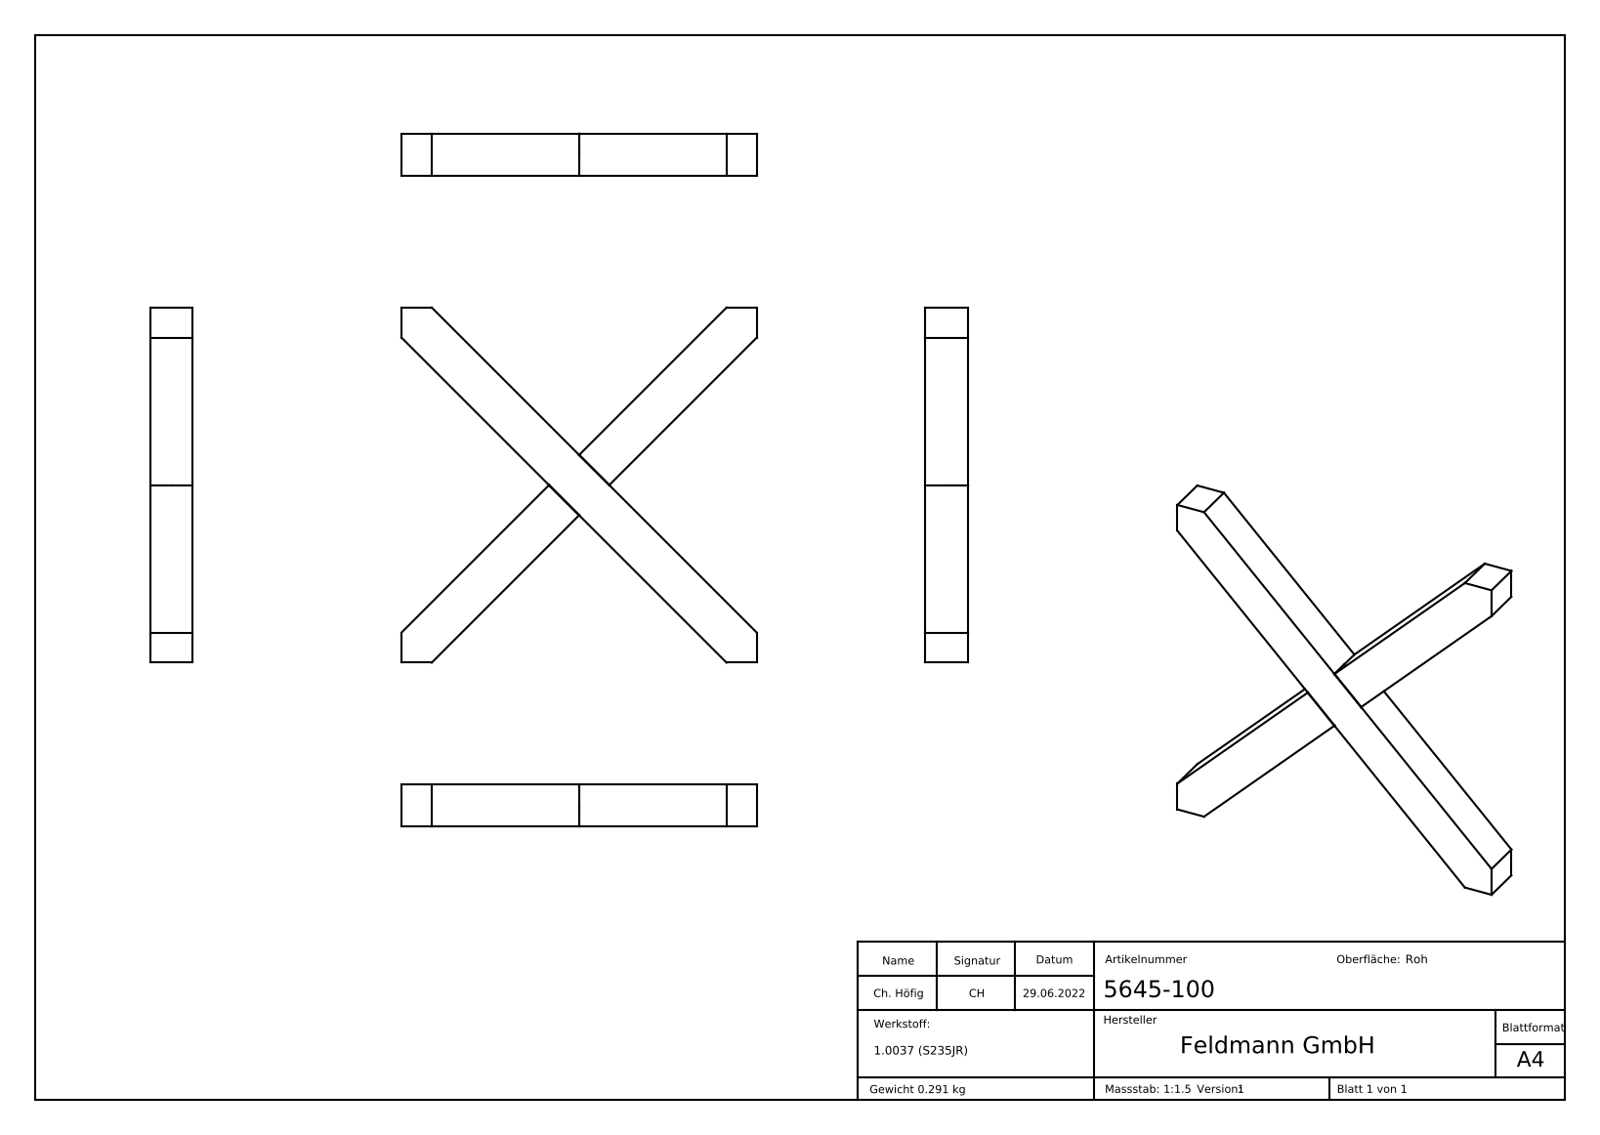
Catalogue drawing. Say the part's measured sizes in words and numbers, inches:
The part is named "5645-100". Its 3-D file was written by "SolidWorks 2018 (CONFIG_CONTROL_DESIGN)". It is 1 solid with 279 faces: 168 planar, 0 cylindrical and 111 other. Overall it measures 3.937 by 3.937 by 0.472 inches. Its volume is 2.274 cubic inches and its surface area 20.08 square inches. The main face-to-face distances are 0.472, 3.937, 0.47, 0.474, 0.476, 0.469, 0.236, 0.478, 0.48, 0.033.
